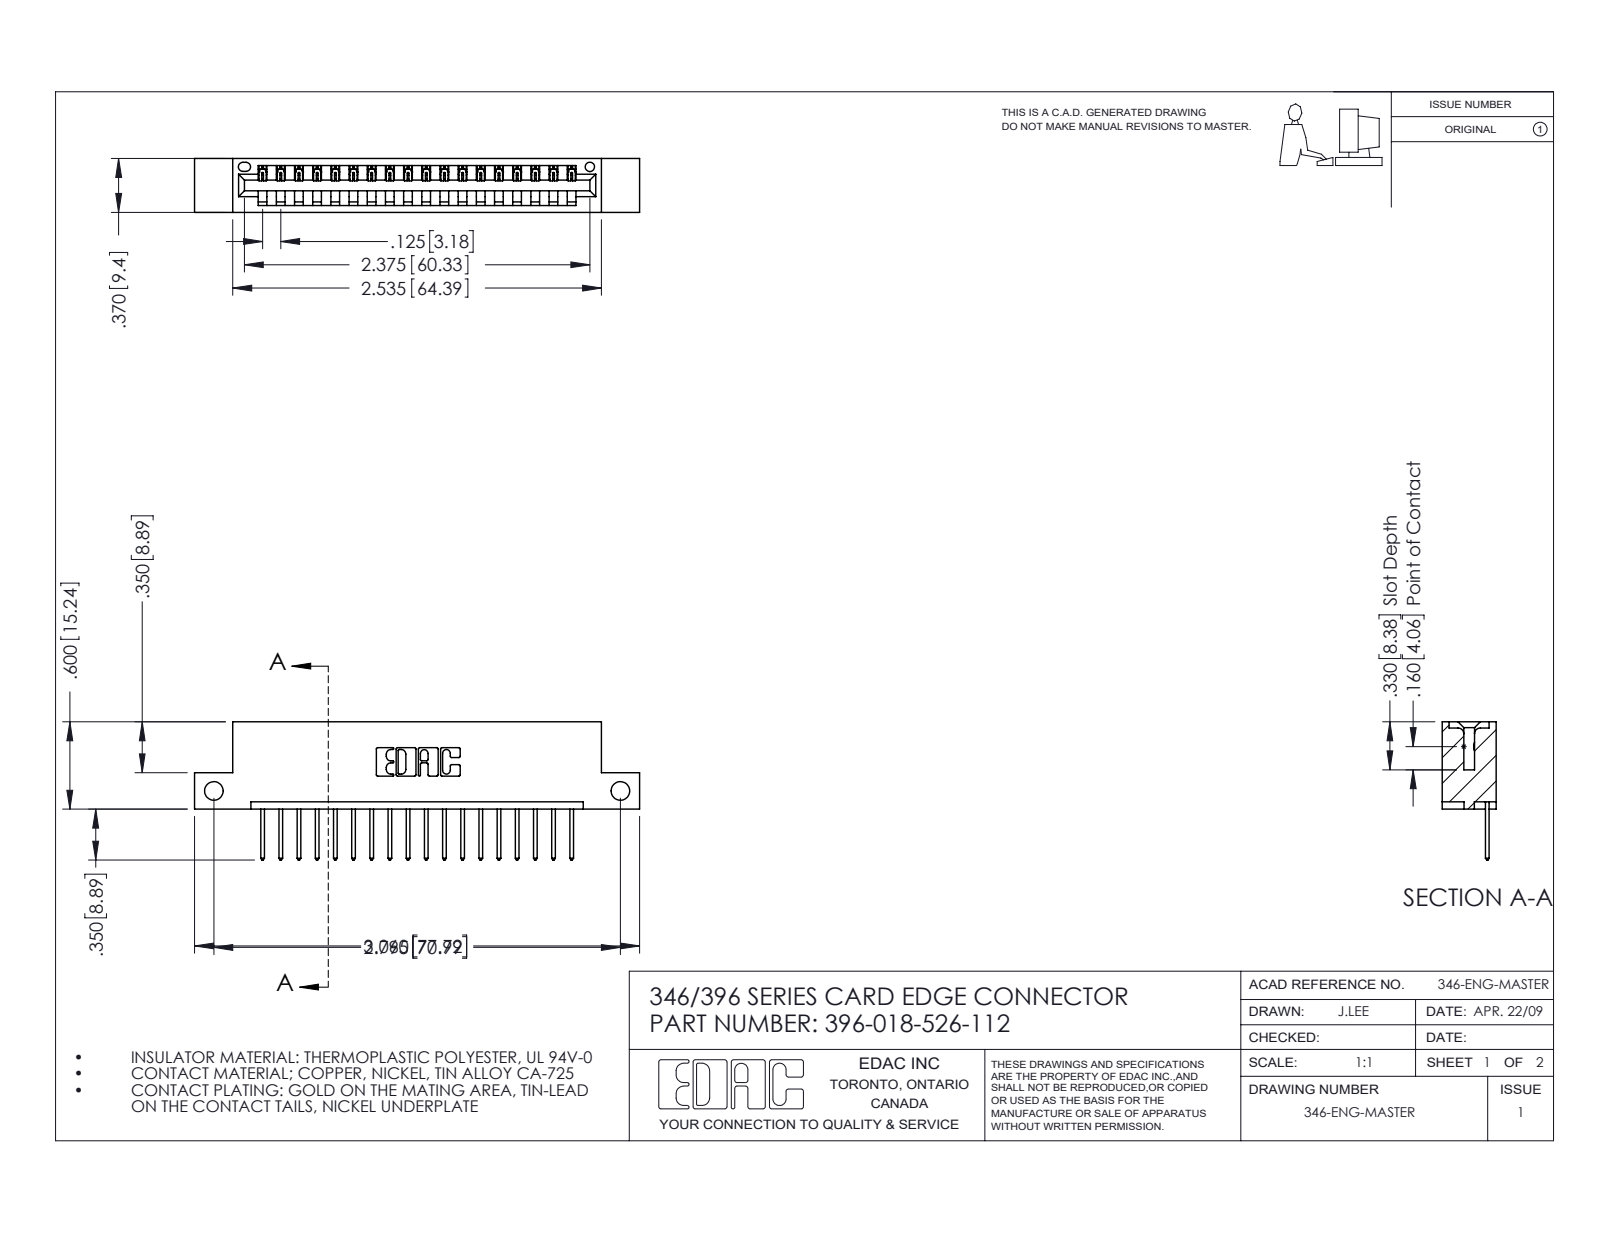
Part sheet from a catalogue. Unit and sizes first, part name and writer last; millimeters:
Units: millimetres
Overall size (bounding box): 77.7 × 24.1 × 9.4
Round holes (diameter × count): ⌀3.3 ×2, ⌀1.6 ×1
Partial cylindrical surfaces — rounded edges, fillets, slot ends (radius × count): R0.2 ×36, R0.3 ×36, R0.3 ×22, R0.2 ×6, R0.8 ×6, R0.7 ×3, R0.8 ×2, R1 ×2
Main face-to-face distances: 1.2, 8.2, 6.4, 9.4, 1.8, 7.6, 0.6, 3.8, 5.6, 2.5
Hole centre spacings: 71
Volume: 7 180 mm³ · Surface area: 8 542 mm²
Bodies: 19 solids, 1166 faces (796 planar, 370 cylindrical, 0 other)
Part name (STEP PRODUCT): 396-018-526-112; 345-292-001_345-293-126; 346 Part_Flush Mounting Lugs - Side Mount
STEP written by: SolidWorks 2016 (CONFIG_CONTROL_DESIGN)
